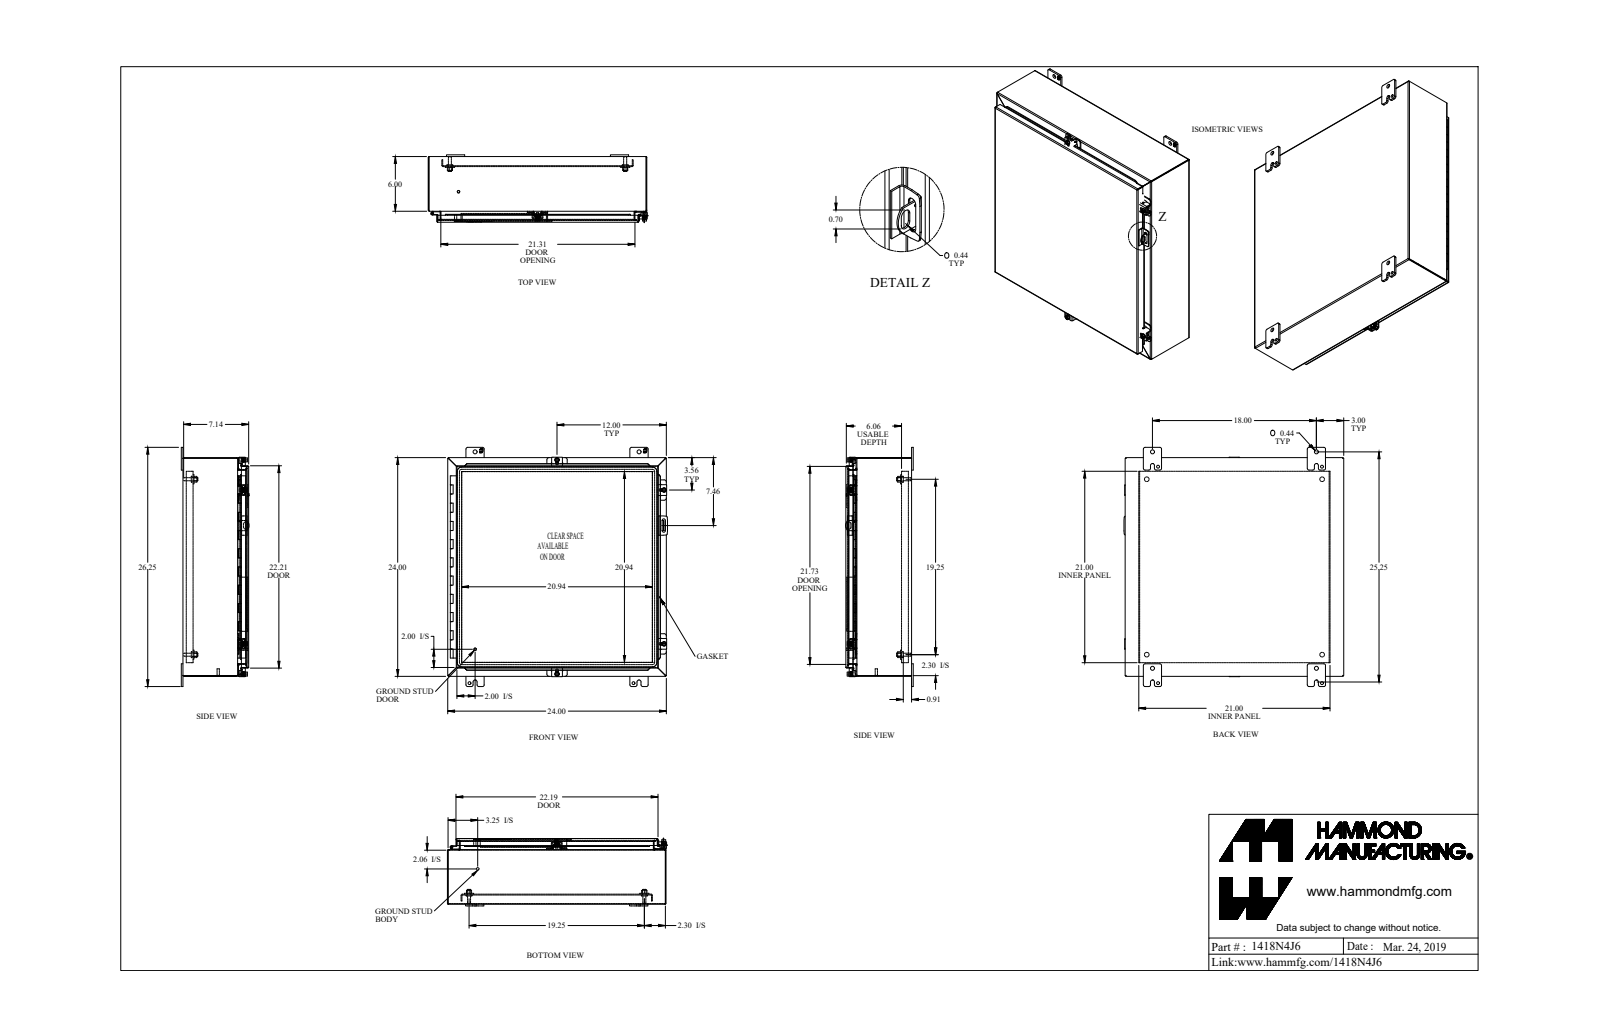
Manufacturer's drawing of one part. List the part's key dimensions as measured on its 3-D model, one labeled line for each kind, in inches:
Part name (STEP PRODUCT): 1418N4J6_Default
STEP written by: SolidWorks 2019 (CONFIG_CONTROL_DESIGN)
Units: inches
Bodies: 40 solids, 1530 faces (928 planar, 515 cylindrical, 87 other)
Overall size (bounding box): 26.25 × 24.126 × 7.437
Volume: 207 in³ · Surface area: 5 347 in²
Round holes (diameter × count): ⌀0.213 ×4, ⌀0.265 ×4, ⌀0.313 ×4, ⌀0.375 ×4, ⌀0.437 ×4, ⌀0.5 ×4, ⌀0.307 ×2, ⌀0.445 ×2, ⌀0.125 ×1, ⌀0.187 ×1, ⌀3.5 ×1
Round bosses / shafts (diameter × count): ⌀0.65 ×4, ⌀0.5 ×4, ⌀0.39 ×4, ⌀0.375 ×4, ⌀0.33 ×4, ⌀0.244 ×4, ⌀1 ×2, ⌀0.281 ×2
Partial cylindrical surfaces — rounded edges, fillets, slot ends (radius × count): R0.25 ×40, R0.188 ×26, R0.036 ×24, R0.108 ×24, R0.048 ×21, R0.143 ×21, R0.06 ×11, R0.125 ×10
Main face-to-face distances: 0.072, 23.928, 0.072, 7.066, 7.138, 7.138, 7.21, 0.095, 6.106, 6.034
Hole centre spacings: 19.25, 18, 23.442, 8.143, 9.857, 9.857, 21.408, 22.259
